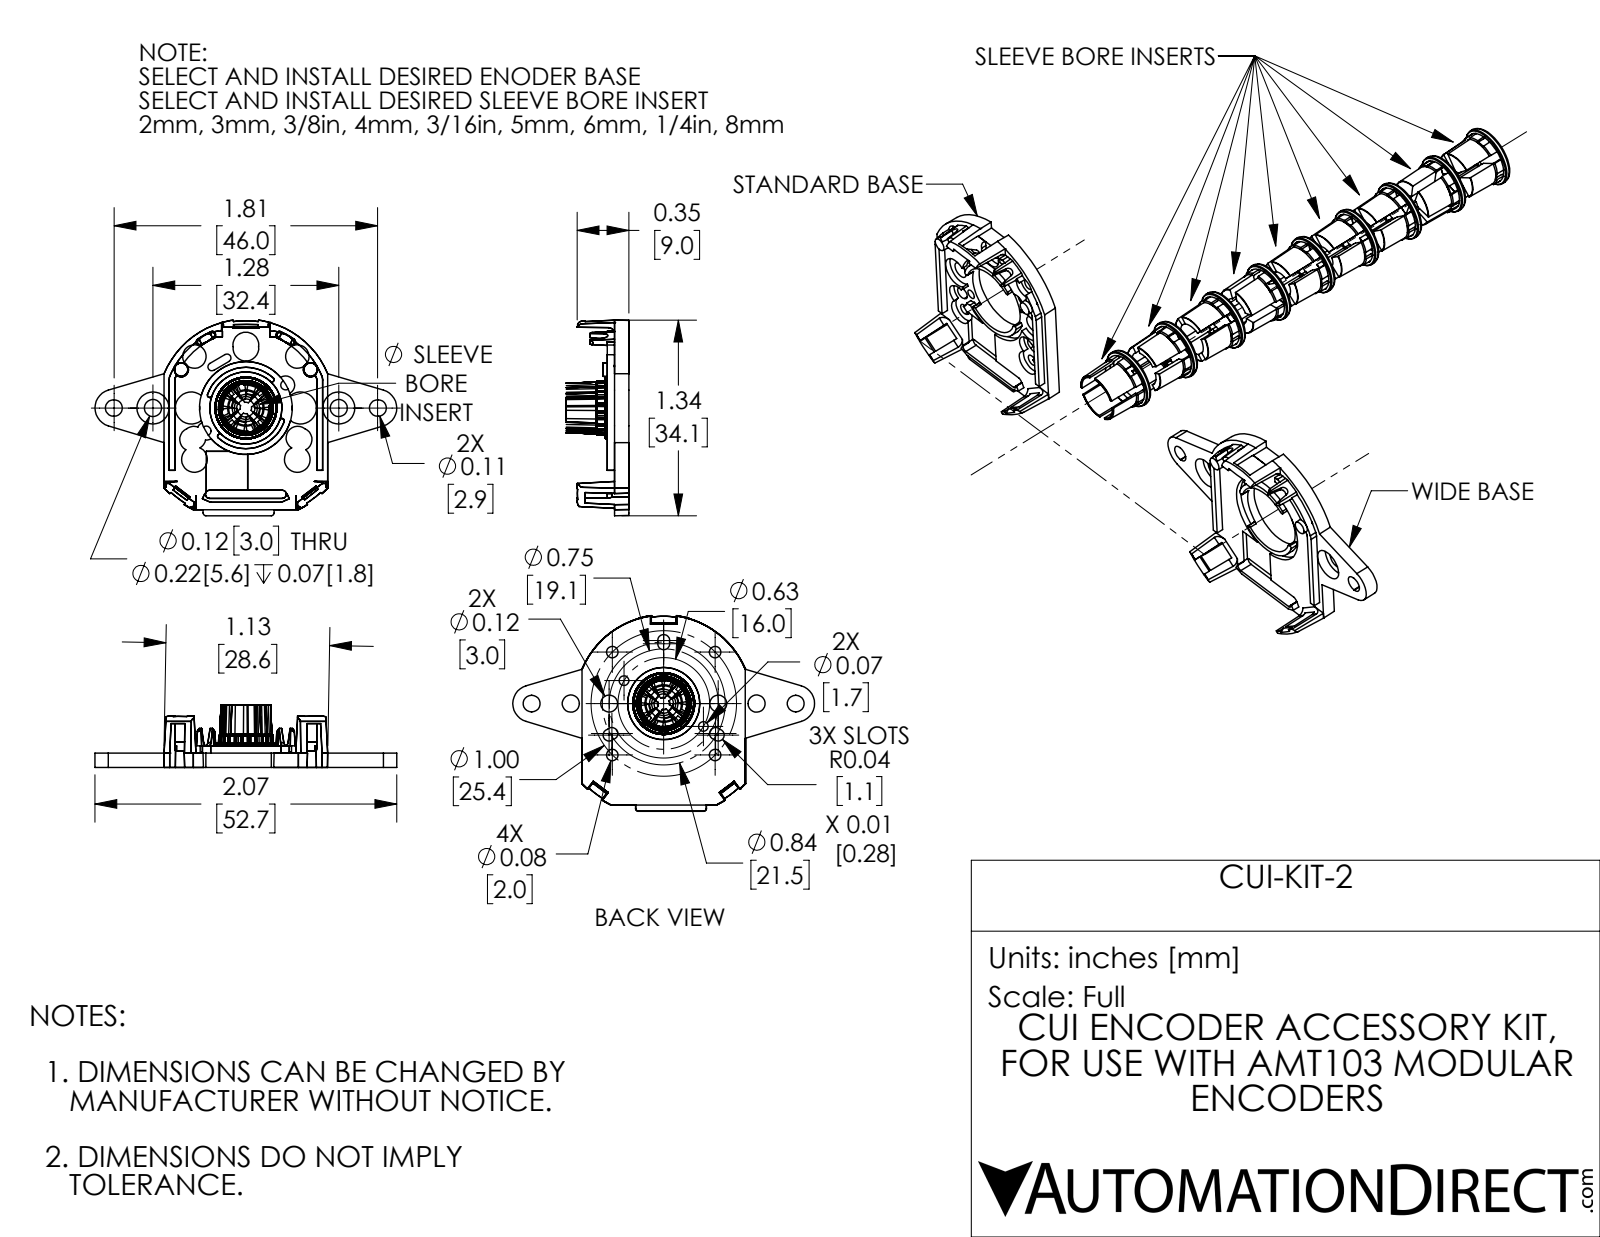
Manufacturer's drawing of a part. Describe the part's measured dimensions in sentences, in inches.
The part is named "CUI-KIT-2". Its 3-D file was written by "SolidWorks 2021 (AUTOMOTIVE_DESIGN)". It is 11 solids with 1365 faces: 444 planar, 346 cylindrical and 575 other. Overall it measures 4.573 by 3.8 by 1.344 inches. Its volume is 0.348 cubic inches and its surface area 15.36 square inches. Round holes: 4 of diameter 0.079, 2 of diameter 0.067, 2 of diameter 0.116, 2 of diameter 0.118, 2 of diameter 0.161, 2 of diameter 0.177, 2 of diameter 0.22, 2 of diameter 0.496, 1 of diameter 0.638. Round bosses or shafts: 1 of diameter 0.413, 1 of diameter 0.356. Partial cylindrical surfaces (rounded edges, fillets, slot ends): 15 of radius 0.039, 9 of radius 0.079, 8 of radius 0.016, 6 of radius 0.041, 4 of radius 0.028, 4 of radius 0.03, 4 of radius 0.056, 4 of radius 0.08. The main face-to-face distances are 0.085, 0.098, 0.183, 0.039, 0.029, 0.013, 0.059, 0.026, 0.124, 0.213. The hole center spacings are 0.354, 0.5, 0.707, 0.188, 0.212, 0.315, 0.517, 0.639.
